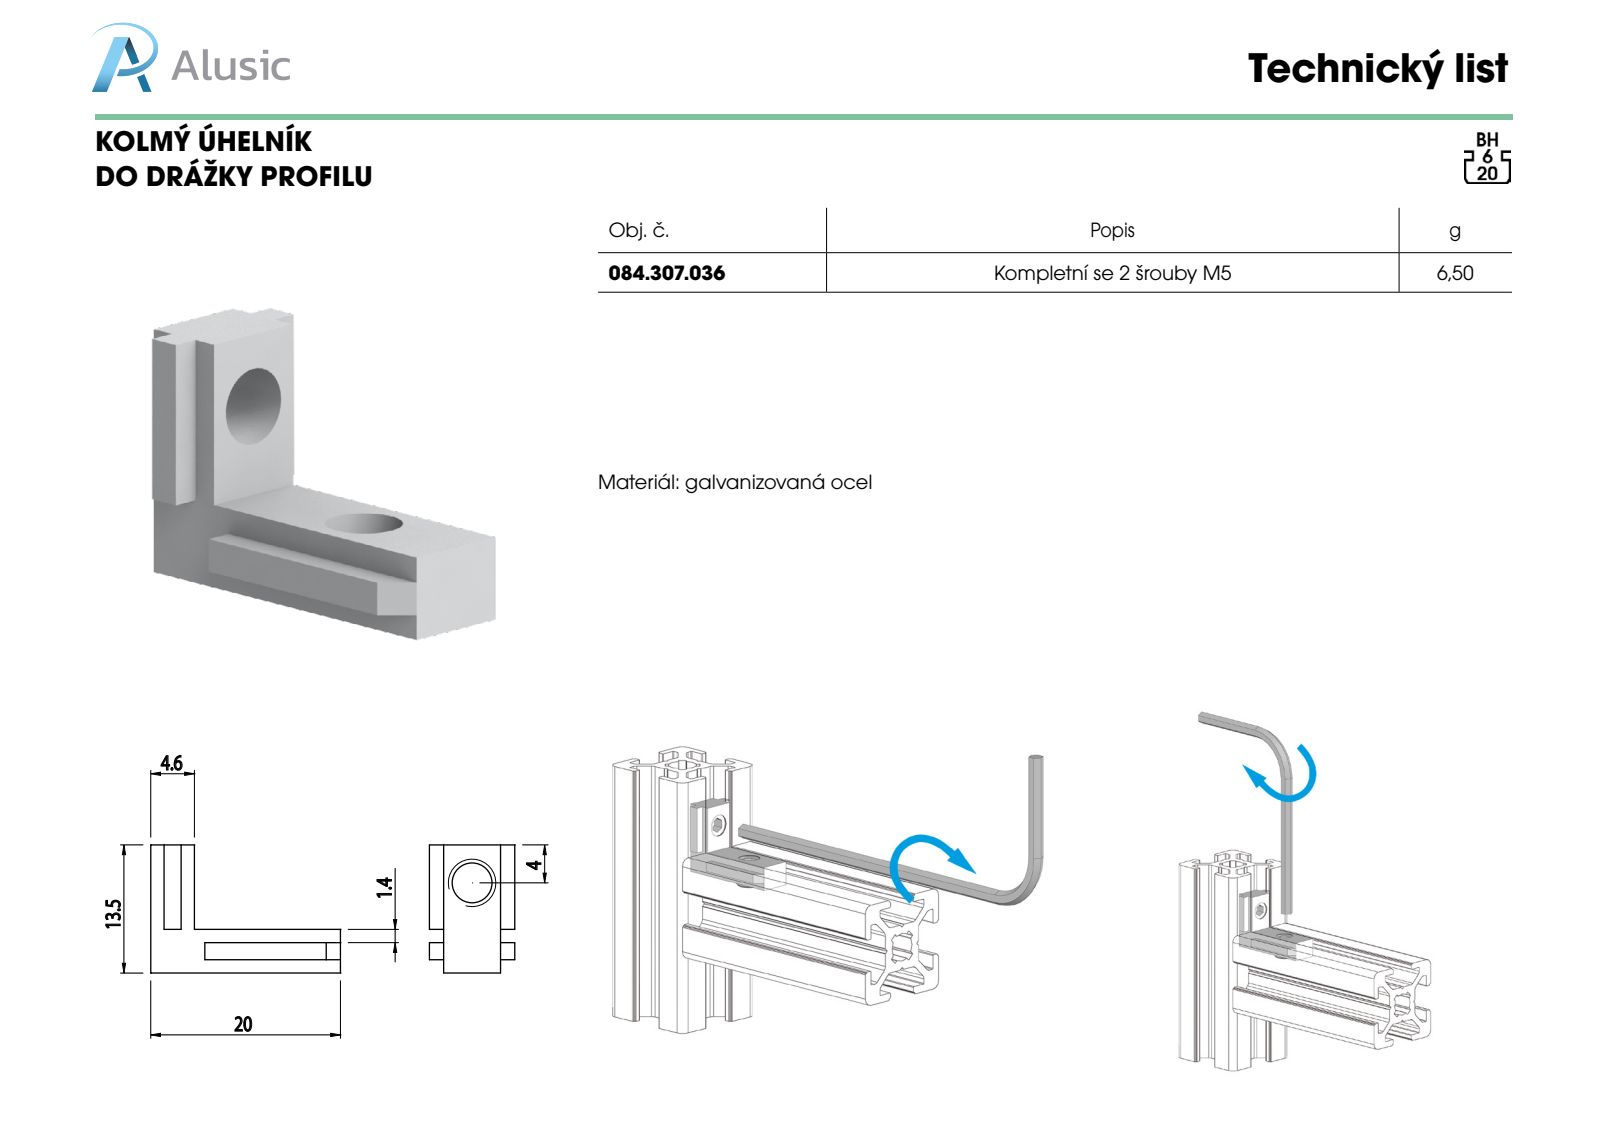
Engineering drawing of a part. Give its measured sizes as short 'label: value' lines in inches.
name: 084.307.036
written by: SolidWorks 2012 (CONFIG_CONTROL_DESIGN)
unit: in
bodies: 1 solid, 30 faces (26 planar, 4 cylindrical, 0 other)
size: 0.787 × 0.531 × 0.354
volume: 0.048 in³; area: 1.37 in²
holes: 2× ⌀0.165
face distances: 0.055, 0.126, 0.181, 0.236, 0.059, 0.295, 0.071, 0.354, 0.531, 0.476
